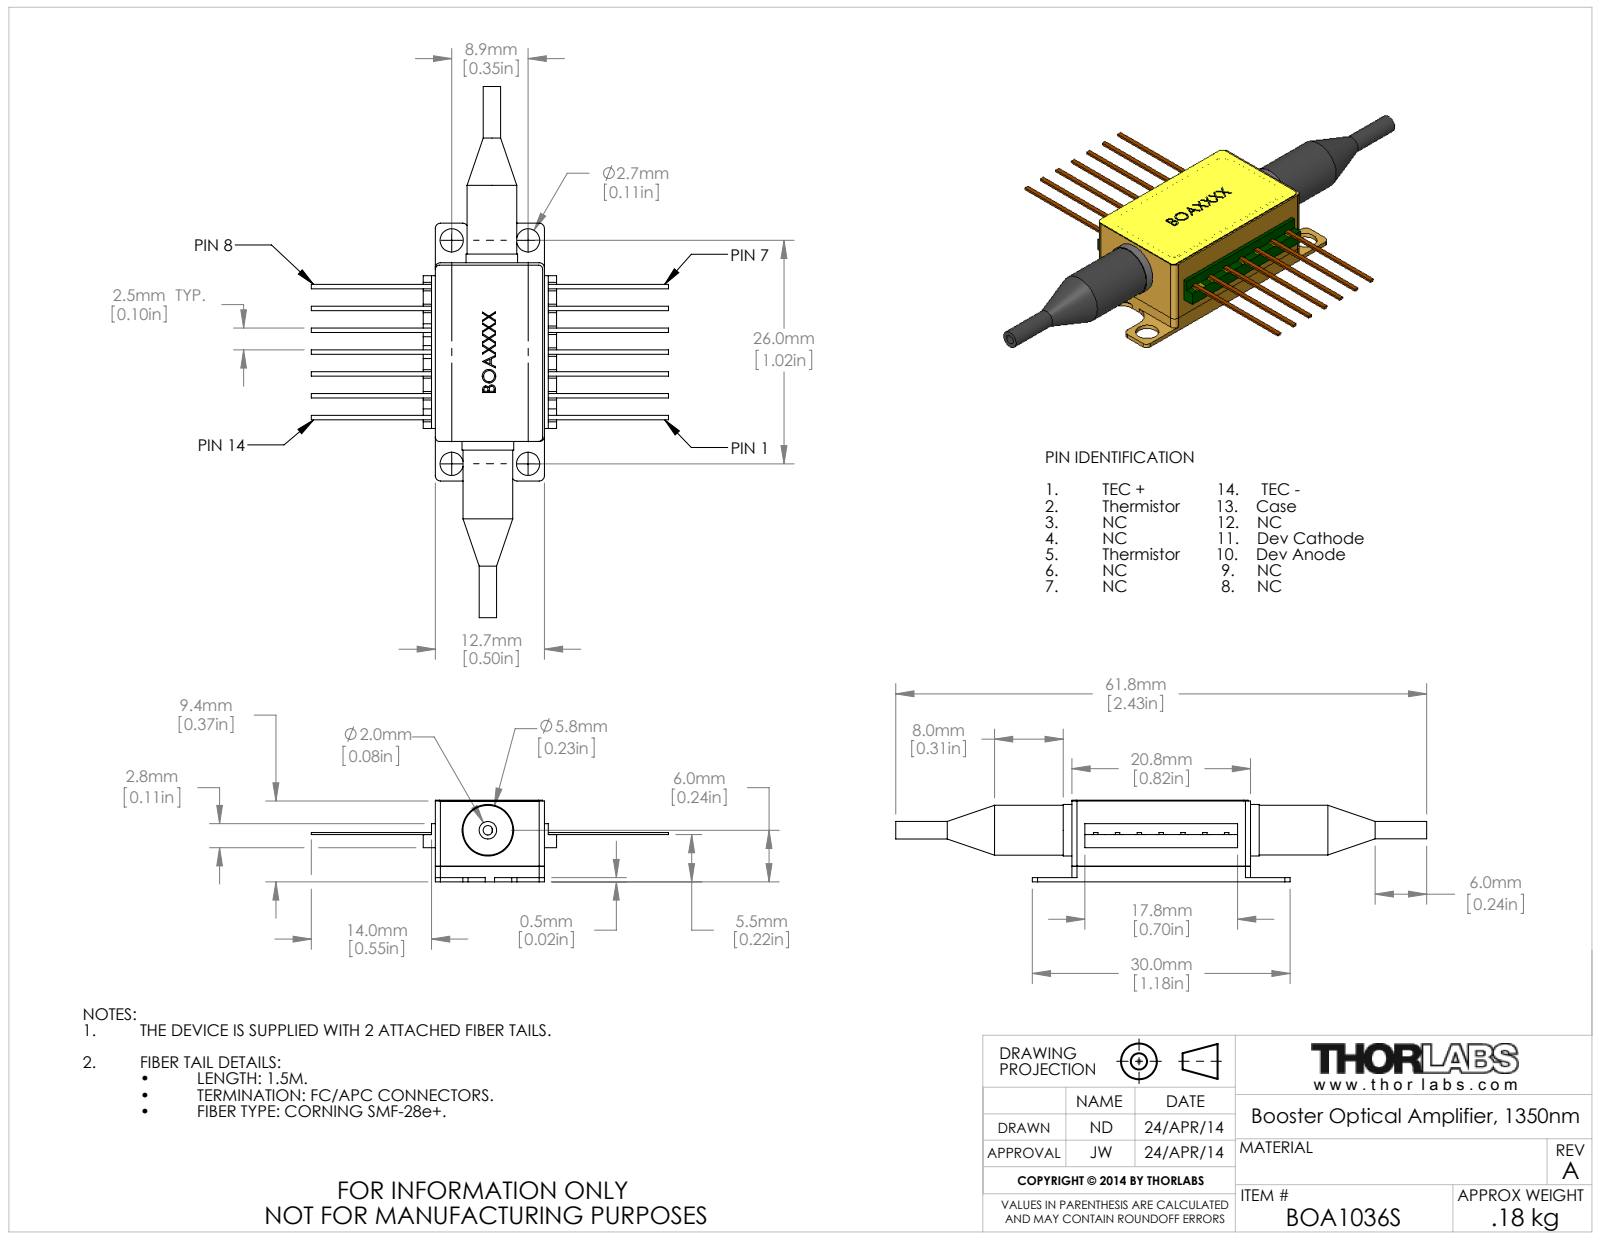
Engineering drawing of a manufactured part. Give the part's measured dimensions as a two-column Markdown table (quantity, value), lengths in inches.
| quantity | value |
| --- | --- |
| part name | QTN007638-E0W |
| STEP written by | SolidWorks 2012 (AUTOMOTIVE_DESIGN) |
| units | inches |
| bodies | 0 solids, 270 faces (204 planar, 48 cylindrical, 18 other) |
| overall size | 2.433 × 1.638 × 0.374 |
| round holes (diameter × count) | 0.106 × 4, 0.043 × 2 |
| round bosses / shafts (diameter × count) | 0.236 × 2, 0.228 × 2, 0.08 × 2 |
| partial cylindrical surfaces (radius × count) | 0.024 × 12, 0.02 × 4, 0.079 × 4 |
| main face-to-face distances | 0.374, 0.5, 0.156, 0.218, 0.217, 0.06, 0.158, 0.02, 0.226, 0.07 |
| hole center spacings | 0.35, 1.024, 1.082, 0.019 |
